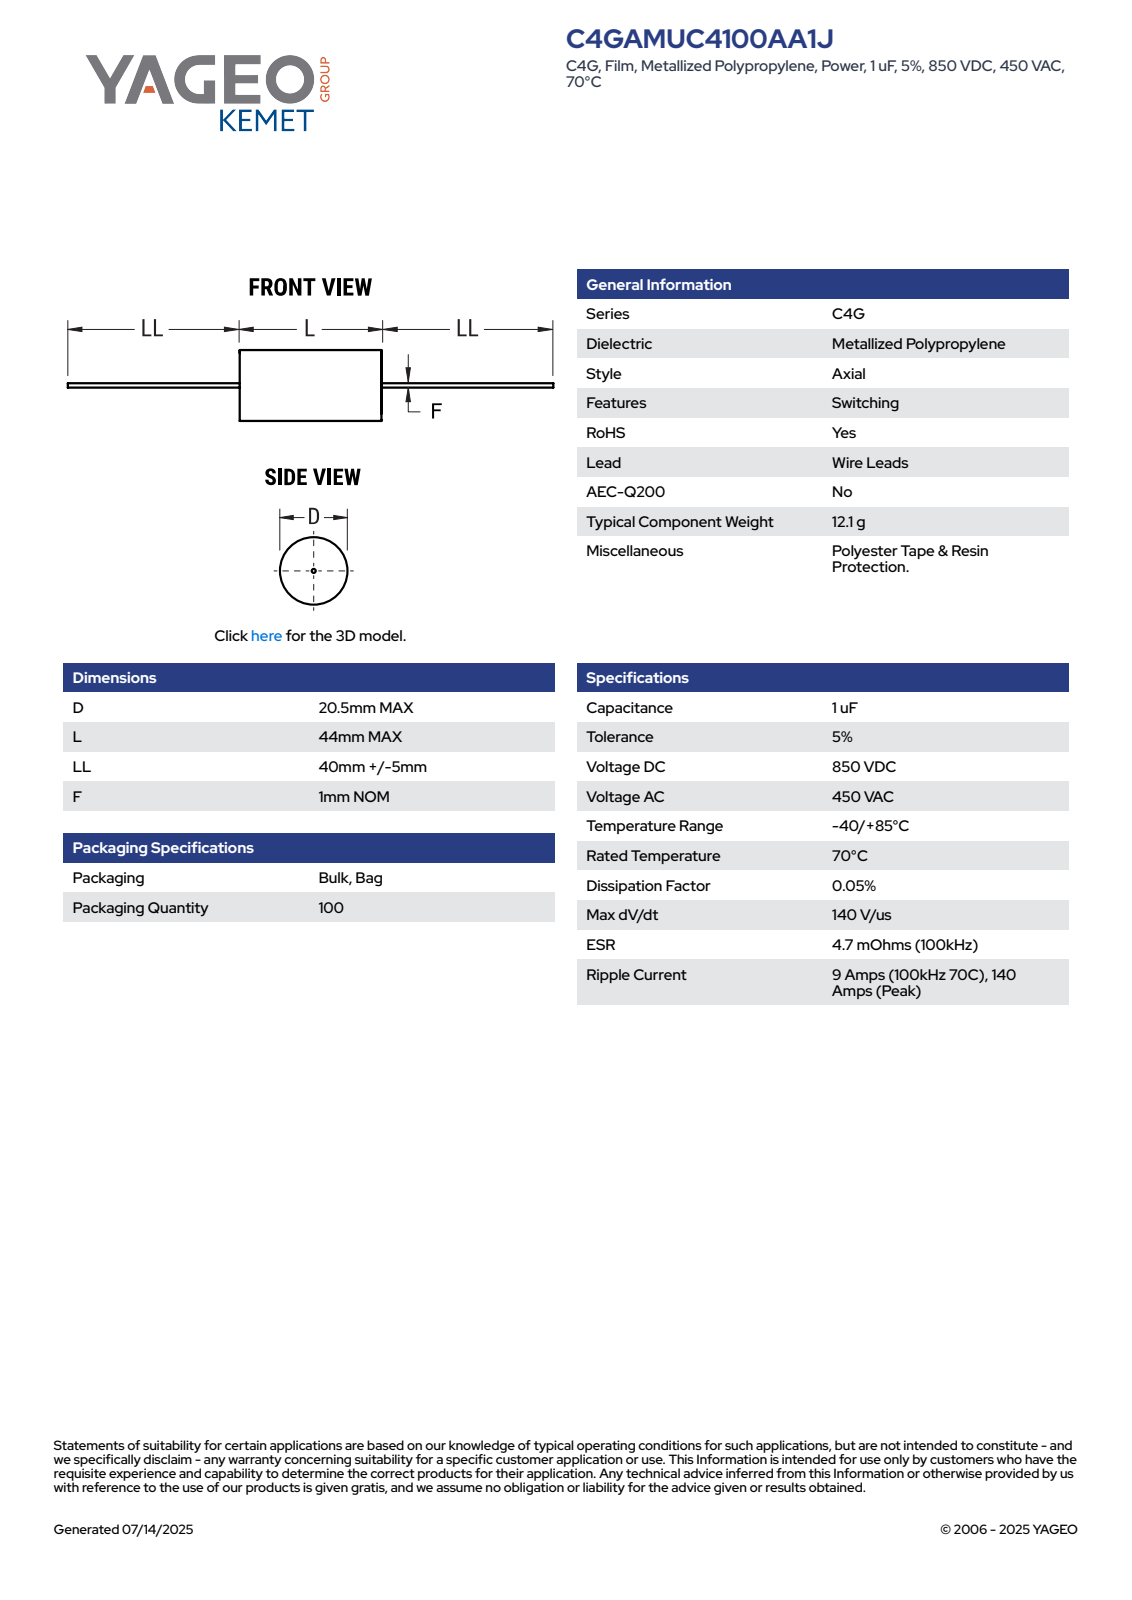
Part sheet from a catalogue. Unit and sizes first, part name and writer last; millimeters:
Units: millimetres
Overall size (bounding box): 134 × 20.5 × 20.5
Round bosses / shafts (diameter × count): ⌀20.5 ×1, ⌀1 ×1
Partial cylindrical surfaces — rounded edges, fillets, slot ends (radius × count): R10.24 ×1
Main face-to-face distances: 44, 43.99, 44.99, 45, 88.99, 134, 89.01, 89, 45.01
Volume: 14 593 mm³ · Surface area: 4 436 mm²
Bodies: 2 solids, 87 faces (28 planar, 28 cylindrical, 31 other)
Part name (STEP PRODUCT): CFP_ACWF_20.5X44_D20.5L44LL45F1
STEP written by: SolidWorks 2014 (AUTOMOTIVE_DESIGN)
